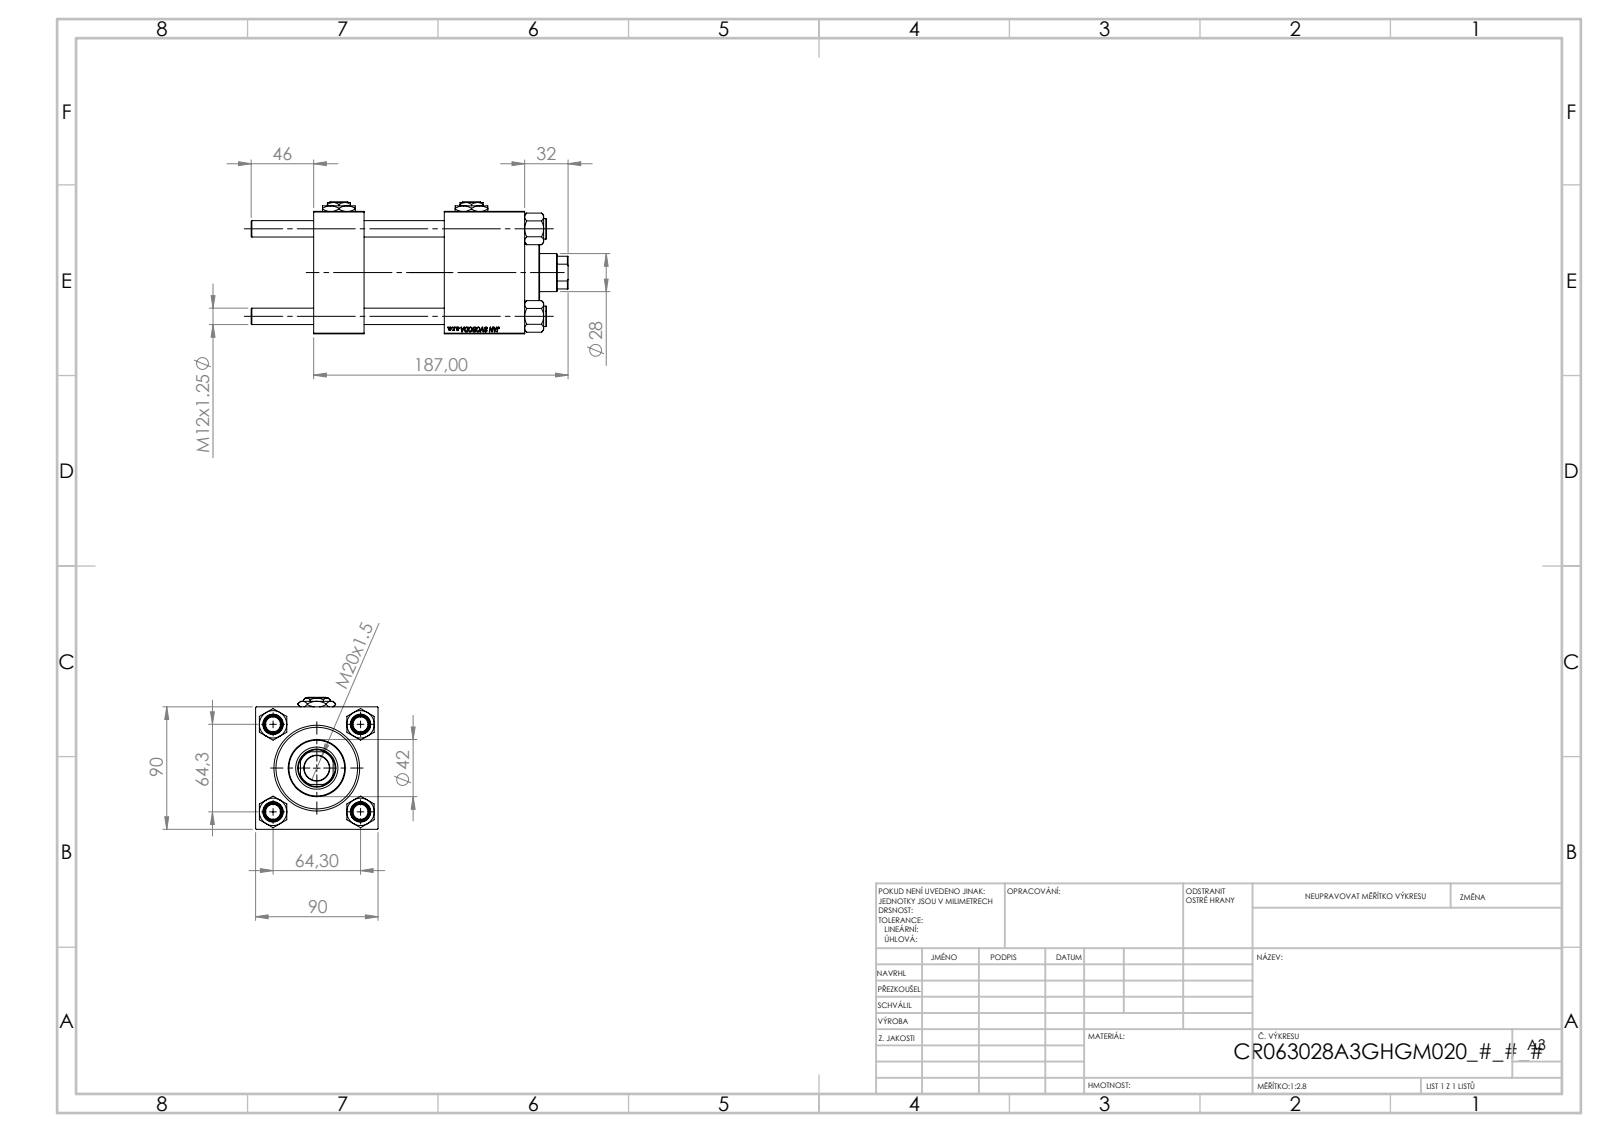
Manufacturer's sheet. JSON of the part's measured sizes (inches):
{"part_name": "V215_VC_A; NUT_M5; Zatka_pro_OIL_PORT; CR025_012_A_0_G_A_G_M_020_+#_##_TYCINKA (+2 more)", "step_written_by": "SolidWorks 2019 (CONFIG_CONTROL_DESIGN)", "units": "inches", "bodies": {"solids": 13, "faces": 1233, "planar": 567, "cylindrical": 88, "other": 578}, "overall_size": [9.173, 3.819, 3.543], "volume_in3": 59.49, "surface_area_in2": 310.1, "round_holes": [[0.472, 4], [0.276, 2], [0.825, 2], [1.181, 2], [0.728, 1], [1.102, 1], [1.22, 1], [1.969, 1], [2.362, 1], [2.48, 1]], "round_bosses_or_shafts": [[0.591, 4], [2.717, 1], [1.654, 1]], "partial_cylinders_radius": [[0.531, 1]], "face_to_face_distances": [3.543, 2.323, 1.457, 4.646, 6.102, 3.78, 4.972, 3.516, 1.193, 1.13], "hole_center_spacings": [1.79, 2.531, 3.58, 3.839]}
